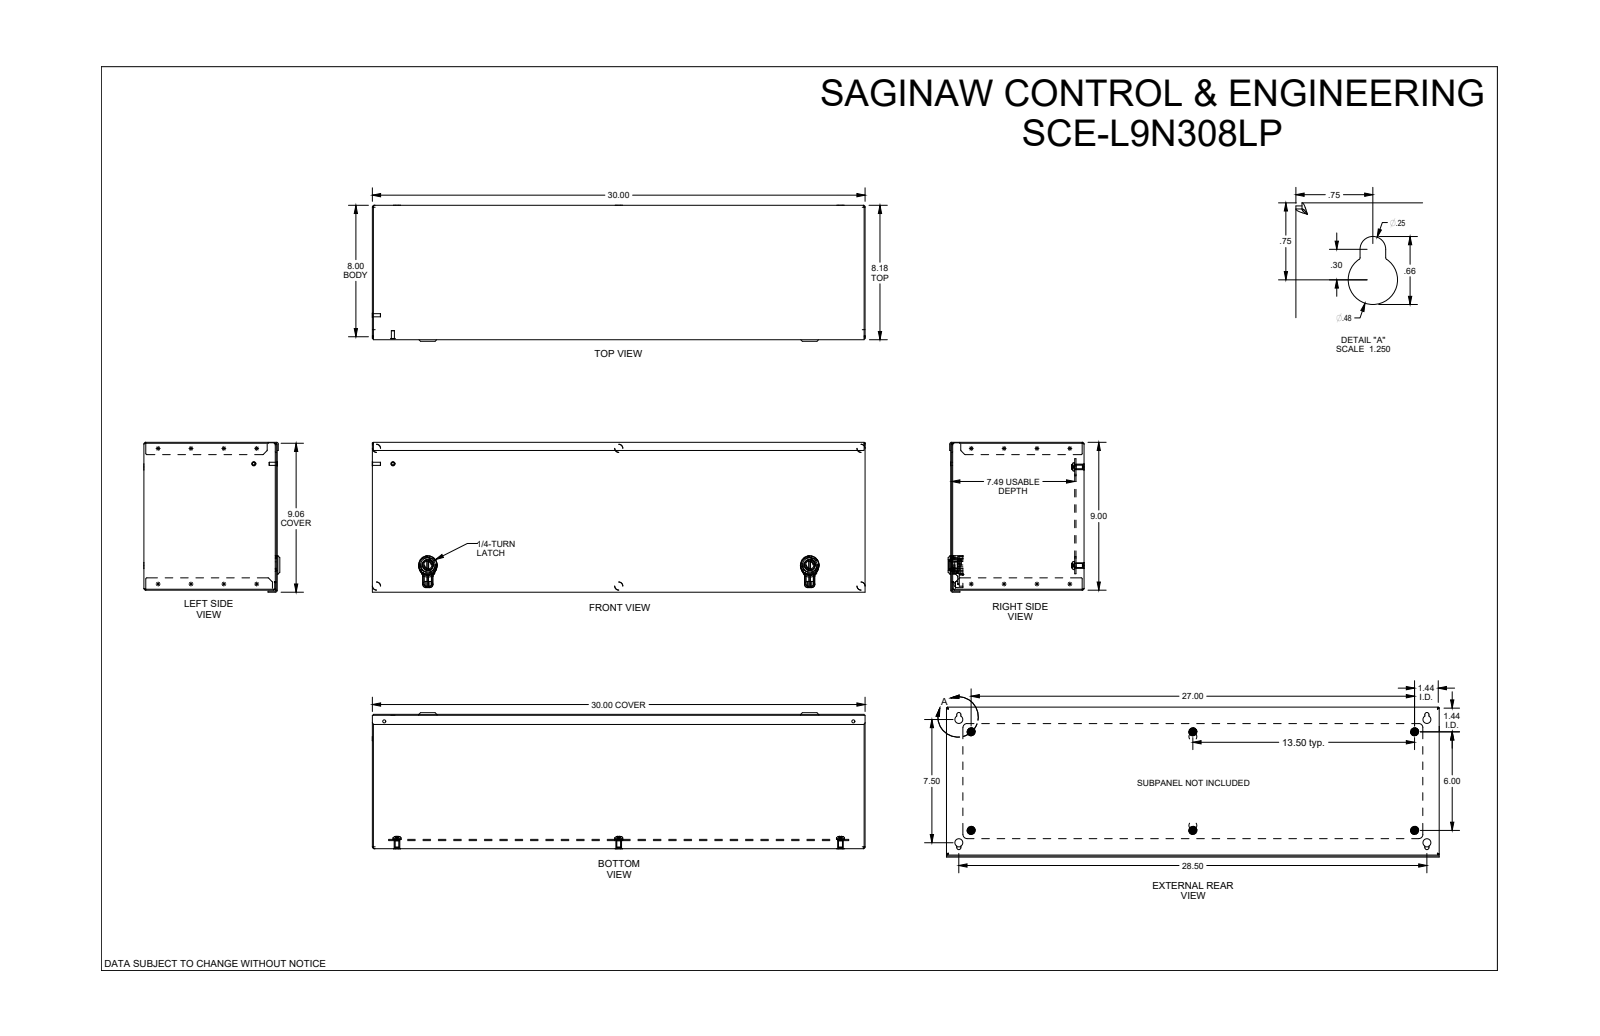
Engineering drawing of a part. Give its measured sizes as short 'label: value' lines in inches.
name: SCE-L9N308LP
written by: SolidWorks 2019 (CONFIG_CONTROL_DESIGN)
unit: in
bodies: 27 solids, 1733 faces (736 planar, 709 cylindrical, 288 other)
size: 30.004 × 9.123 × 8.281
volume: 90.71 in³; area: 2 929 in²
holes: 6× ⌀0.25, 6× ⌀0.343, 4× ⌀0.281, 4× ⌀0.48, 2× ⌀0.188, 2× ⌀0.193, 2× ⌀0.44, 2× ⌀0.635, 2× ⌀0.891
bosses: 6× ⌀0.5, 6× ⌀0.492, 6× ⌀0.341, 6× ⌀0.248, 2× ⌀1.125, 2× ⌀1.125, 2× ⌀0.74, 2× ⌀0.62
rounds: 362× R0.01, 22× R0.015, 16× R0.02, 12× R0.052, 12× R0.055, 12× R0.06, 12× R0.112, 10× R0.125
face distances: 0.06, 8.94, 0.06, 8, 8.12, 8.06, 8.06, 8.88, 9, 7.565
hole spacings: 1.061, 6.792, 13.5, 14.27, 14.773, 15.768, 27.76, 28.559
